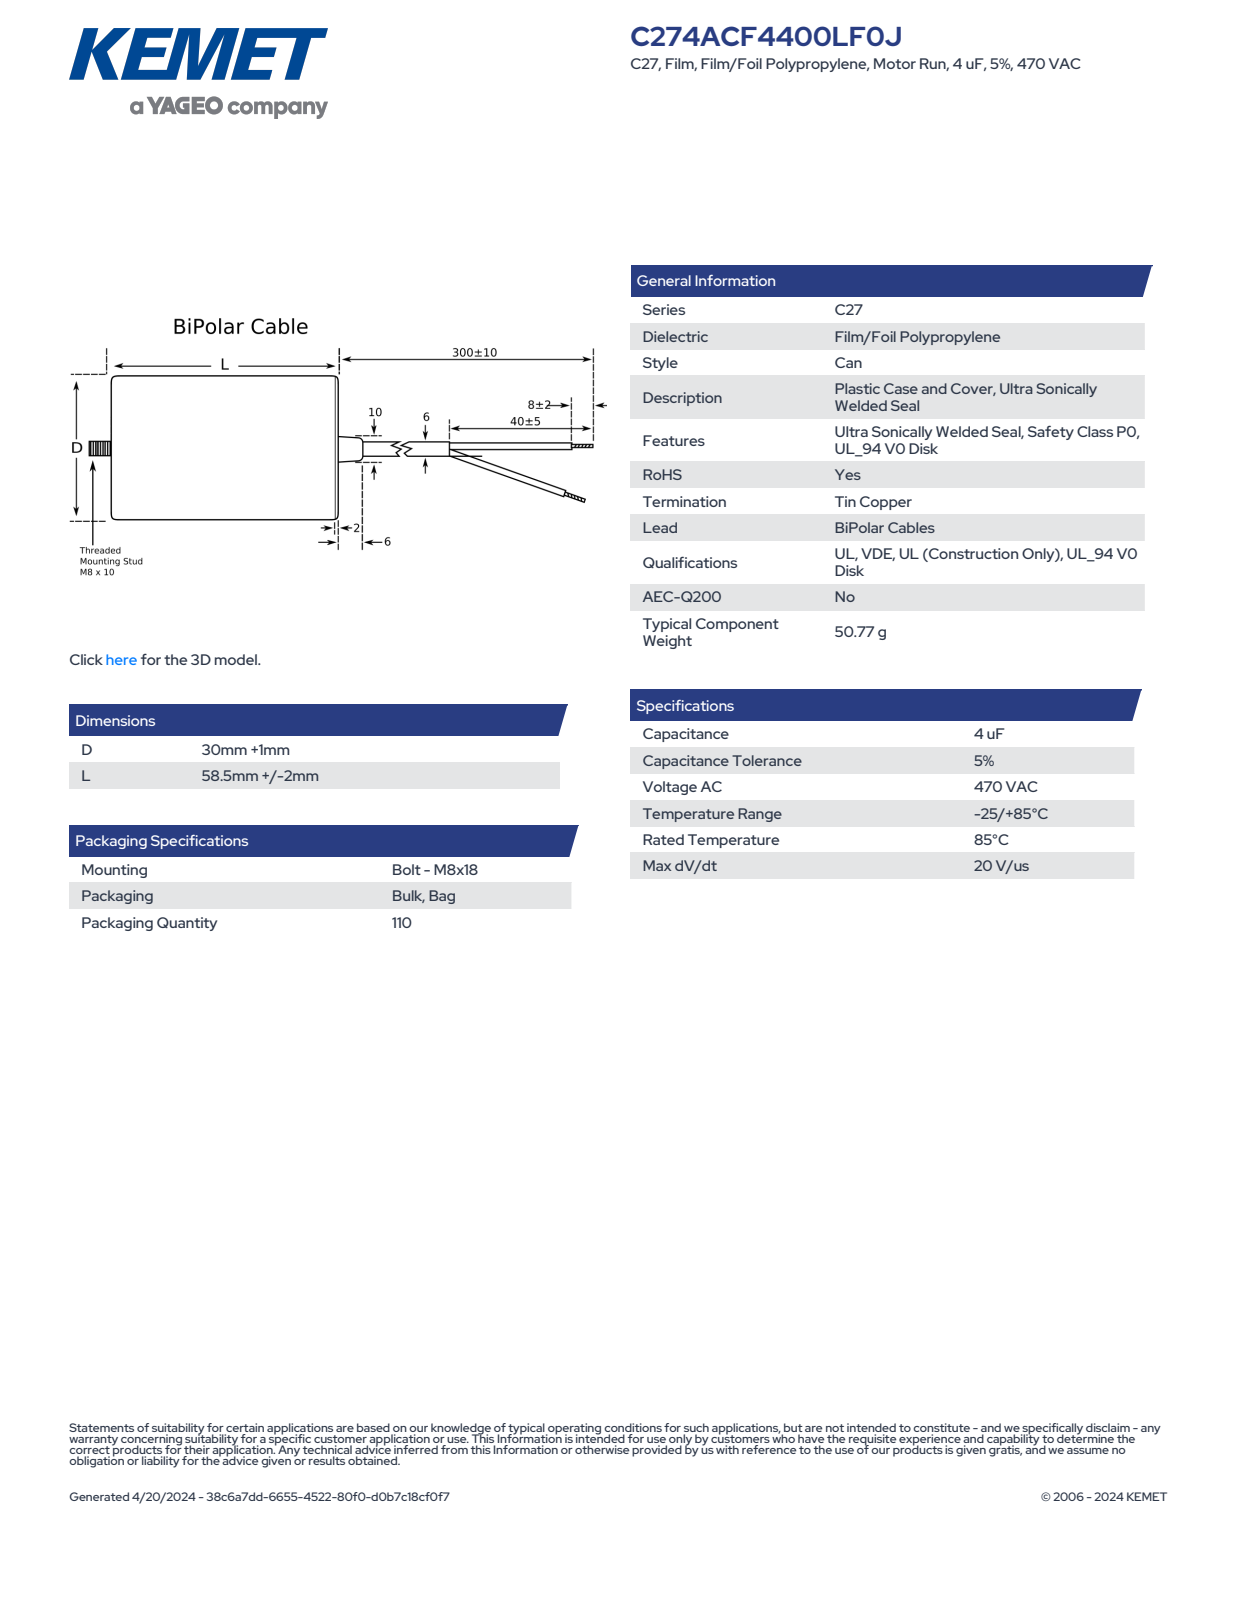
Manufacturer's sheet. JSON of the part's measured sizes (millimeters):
{"part_name": "CFM_KC27BI_30X58.5_D31L60.5", "step_written_by": "SolidWorks 2014 (AUTOMOTIVE_DESIGN)", "units": "millimeters", "bodies": {"solids": 2, "faces": 82, "planar": 28, "cylindrical": 15, "other": 39}, "overall_size": [76.5, 31.01, 31], "volume_mm3": 45361, "surface_area_mm2": 8033, "round_holes": [[27, 1]], "round_bosses_or_shafts": [[31, 1], [8, 1]], "partial_cylinders_radius": [[15.51, 1]], "face_to_face_distances": [58.5, 60.5, 2, 10, 68.5, 70.5, 76.5, 66.5, 8, 6]}
